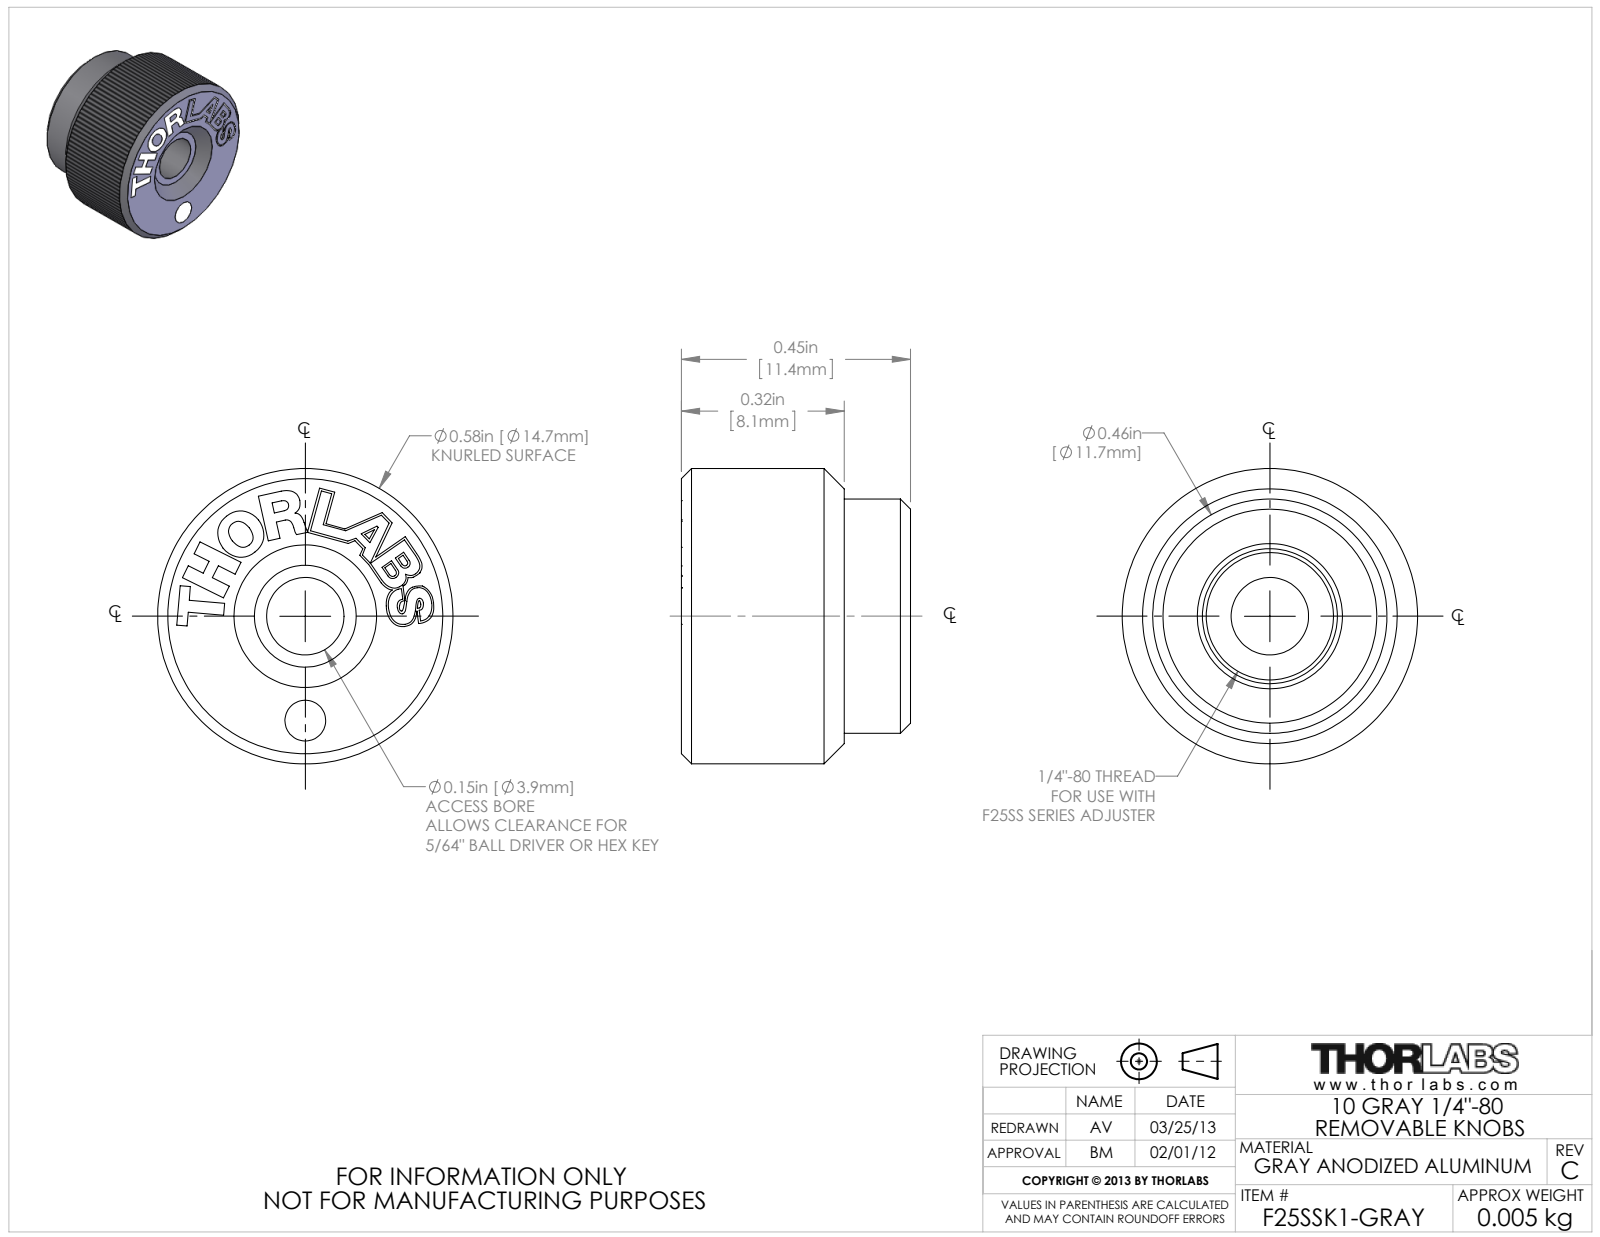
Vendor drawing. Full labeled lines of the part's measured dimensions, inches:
Part name (STEP PRODUCT): 23392-E0W
STEP written by: SolidWorks 2012 (AUTOMOTIVE_DESIGN)
Units: inches
Bodies: 1 solid, 210 faces (118 planar, 21 cylindrical, 71 other)
Overall size (bounding box): 0.58 × 0.58 × 0.45
Volume: 0.088 in³ · Surface area: 1.477 in²
Round holes (diameter × count): ⌀0.08 ×1, ⌀0.152 ×1, ⌀0.25 ×1, ⌀0.265 ×1, ⌀0.29 ×1
Round bosses / shafts (diameter × count): ⌀0.58 ×1, ⌀0.46 ×1
Partial cylindrical surfaces — rounded edges, fillets, slot ends (radius × count): R0.014 ×1, R0.047 ×1, R0.059 ×1
Main face-to-face distances: 0.45, 0.27, 0.18, 0.05, 0.32, 0.13, 0.02, 0.3, 0.03, 0.15
Hole centre spacings: 0.205
